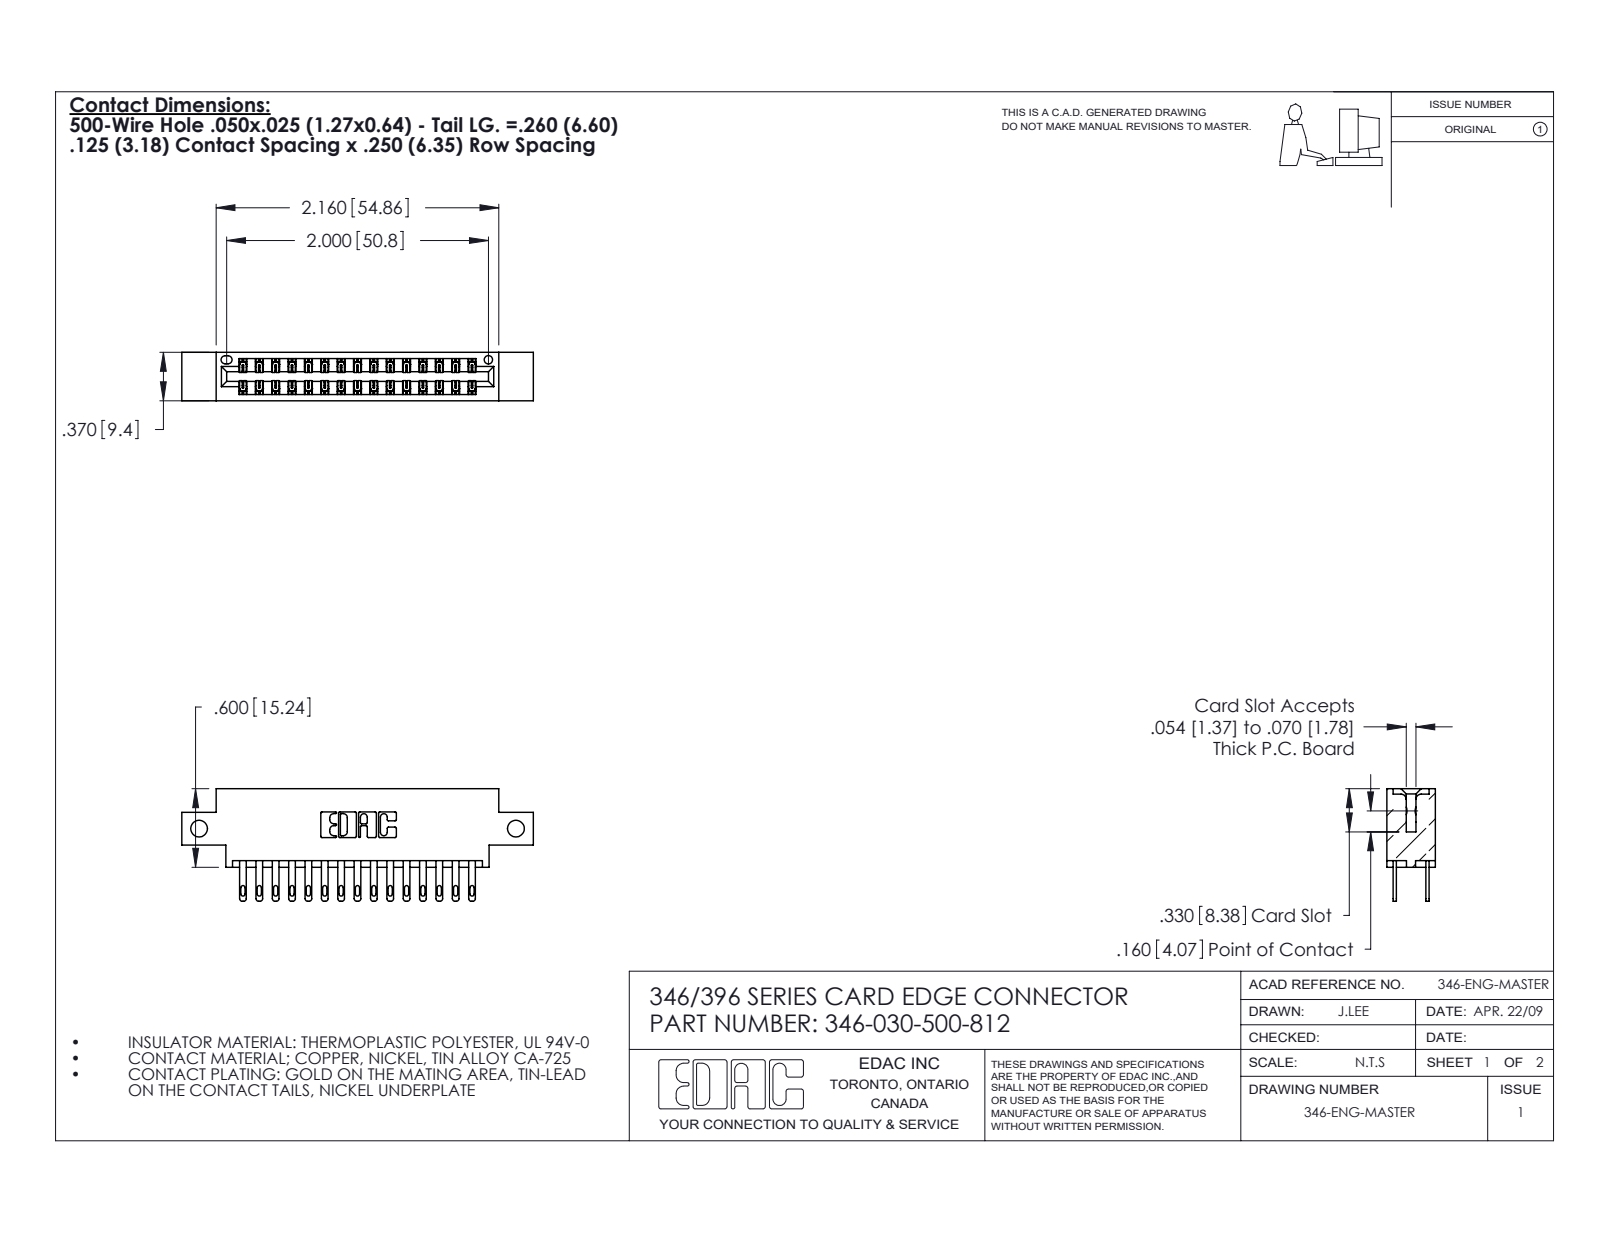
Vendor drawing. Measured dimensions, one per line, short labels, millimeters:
name: 346-030-500-812; 346 Part_0.170 Offset - Side Mount; 345-292-001_345-293-100
written by: SolidWorks 2020 (CONFIG_CONTROL_DESIGN)
unit: mm
bodies: 31 solids, 1566 faces (950 planar, 616 cylindrical, 0 other)
size: 68.2 × 21.8 × 9.4
volume: 6 290 mm³; area: 8 581 mm²
holes: 2× ⌀3.3, 1× ⌀1.6
rounds: 45× R0.2, 30× R0.4, 30× R0.5, 22× R0.3, 6× R0.2, 6× R0.8, 3× R0.7, 2× R0.4
face distances: 1.2, 8.2, 6.4, 9.4, 1.8, 7.6, 0.6, 7, 3.8, 5.6
hole spacings: 61.5
